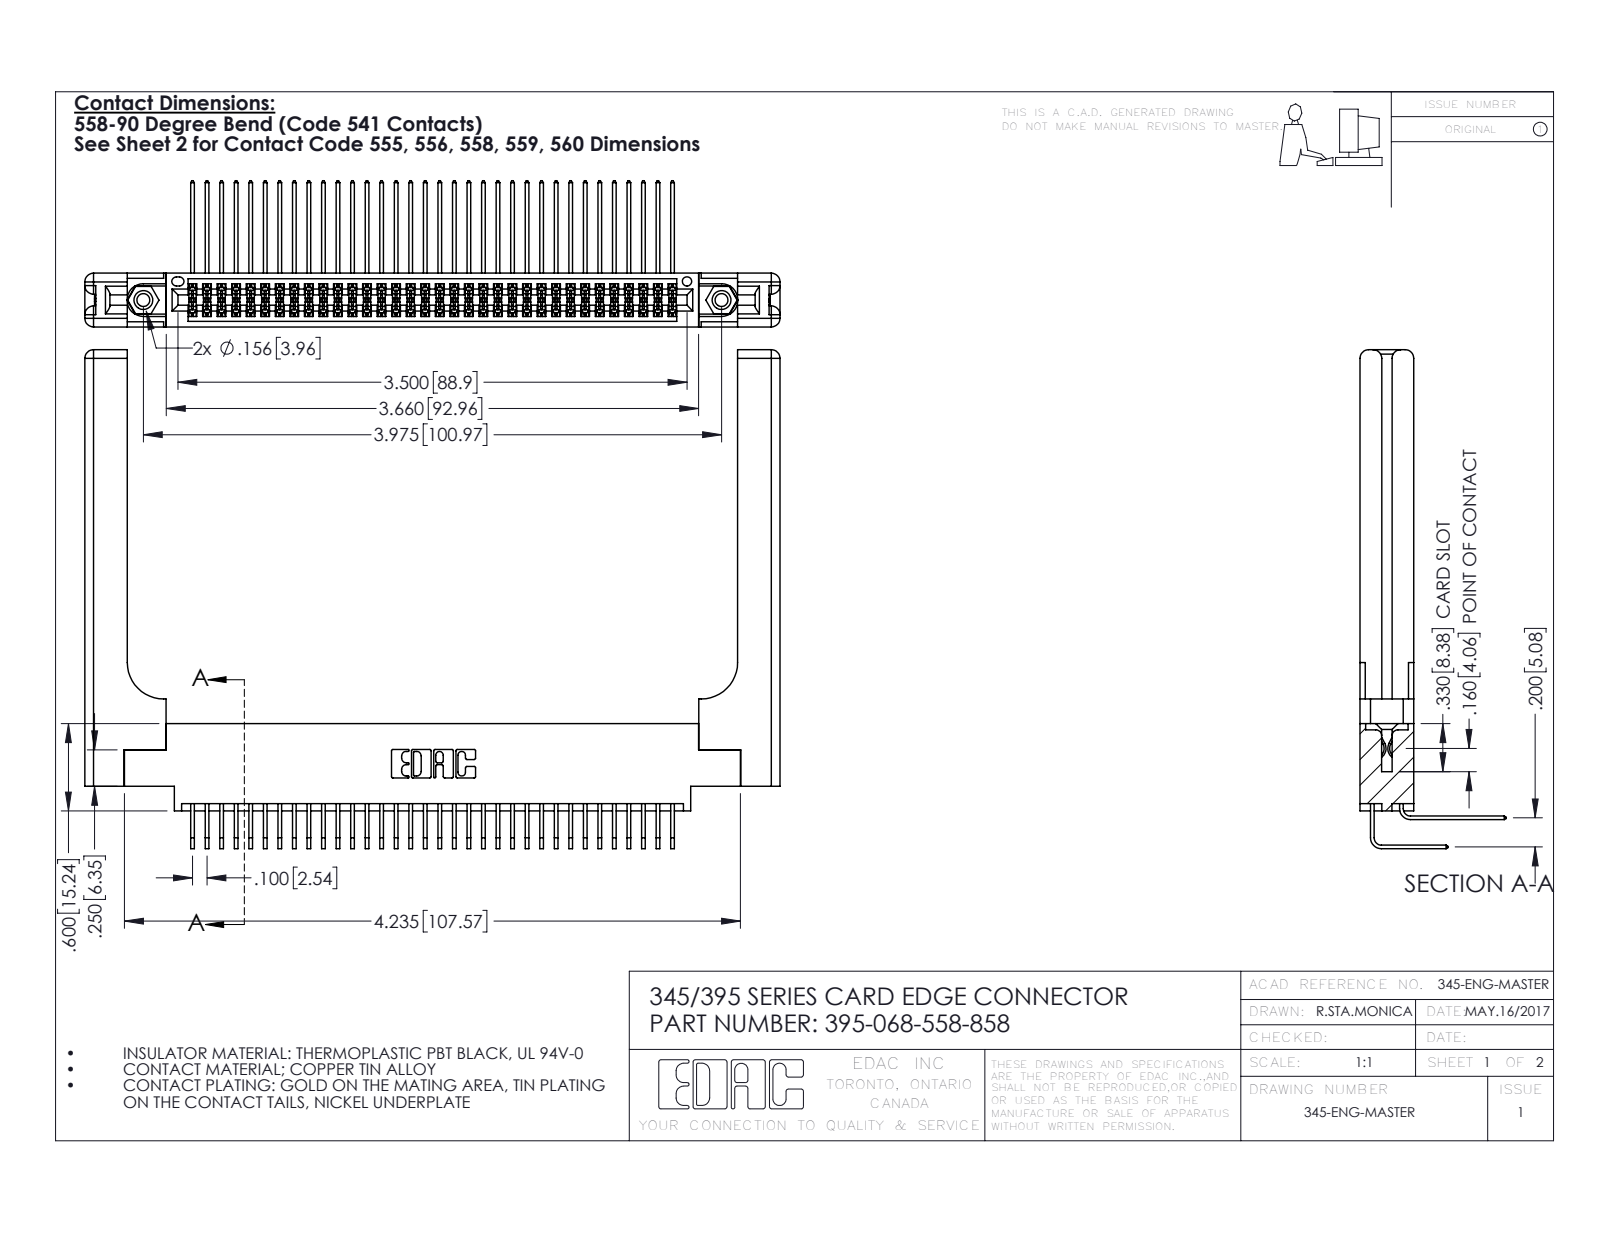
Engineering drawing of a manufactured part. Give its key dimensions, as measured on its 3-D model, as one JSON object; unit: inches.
{"part_name": "395-068-558-858; 345-220-058_345-220-058; 345-250-001_345-250-001-102; 345 Part_0.170 Offset - 0.156 Dia-TH (+2 more)", "step_written_by": "SolidWorks 2016 (CONFIG_CONTROL_DESIGN)", "units": "inches", "bodies": {"solids": 73, "faces": 3922, "planar": 2612, "cylindrical": 1250, "other": 60}, "overall_size": [4.779, 3.429, 1.005], "volume_in3": 1.249, "surface_area_in2": 38.17, "round_holes": [[0.089, 2], [0.125, 2], [0.156, 2], [0.064, 1]], "round_bosses_or_shafts": [[0.155, 2]], "partial_cylinders_radius": [[0.006, 103], [0.01, 22], [0.06, 16], [0.007, 6], [0.031, 6], [0.026, 3], [0.014, 2], [0.019, 2]], "face_to_face_distances": [0.37, 0.072, 0.298, 0.2, 0.098, 0.272, 0.025, 0.225, 0.148, 0.15], "hole_center_spacings": [0.27, 3.74, 3.975]}
